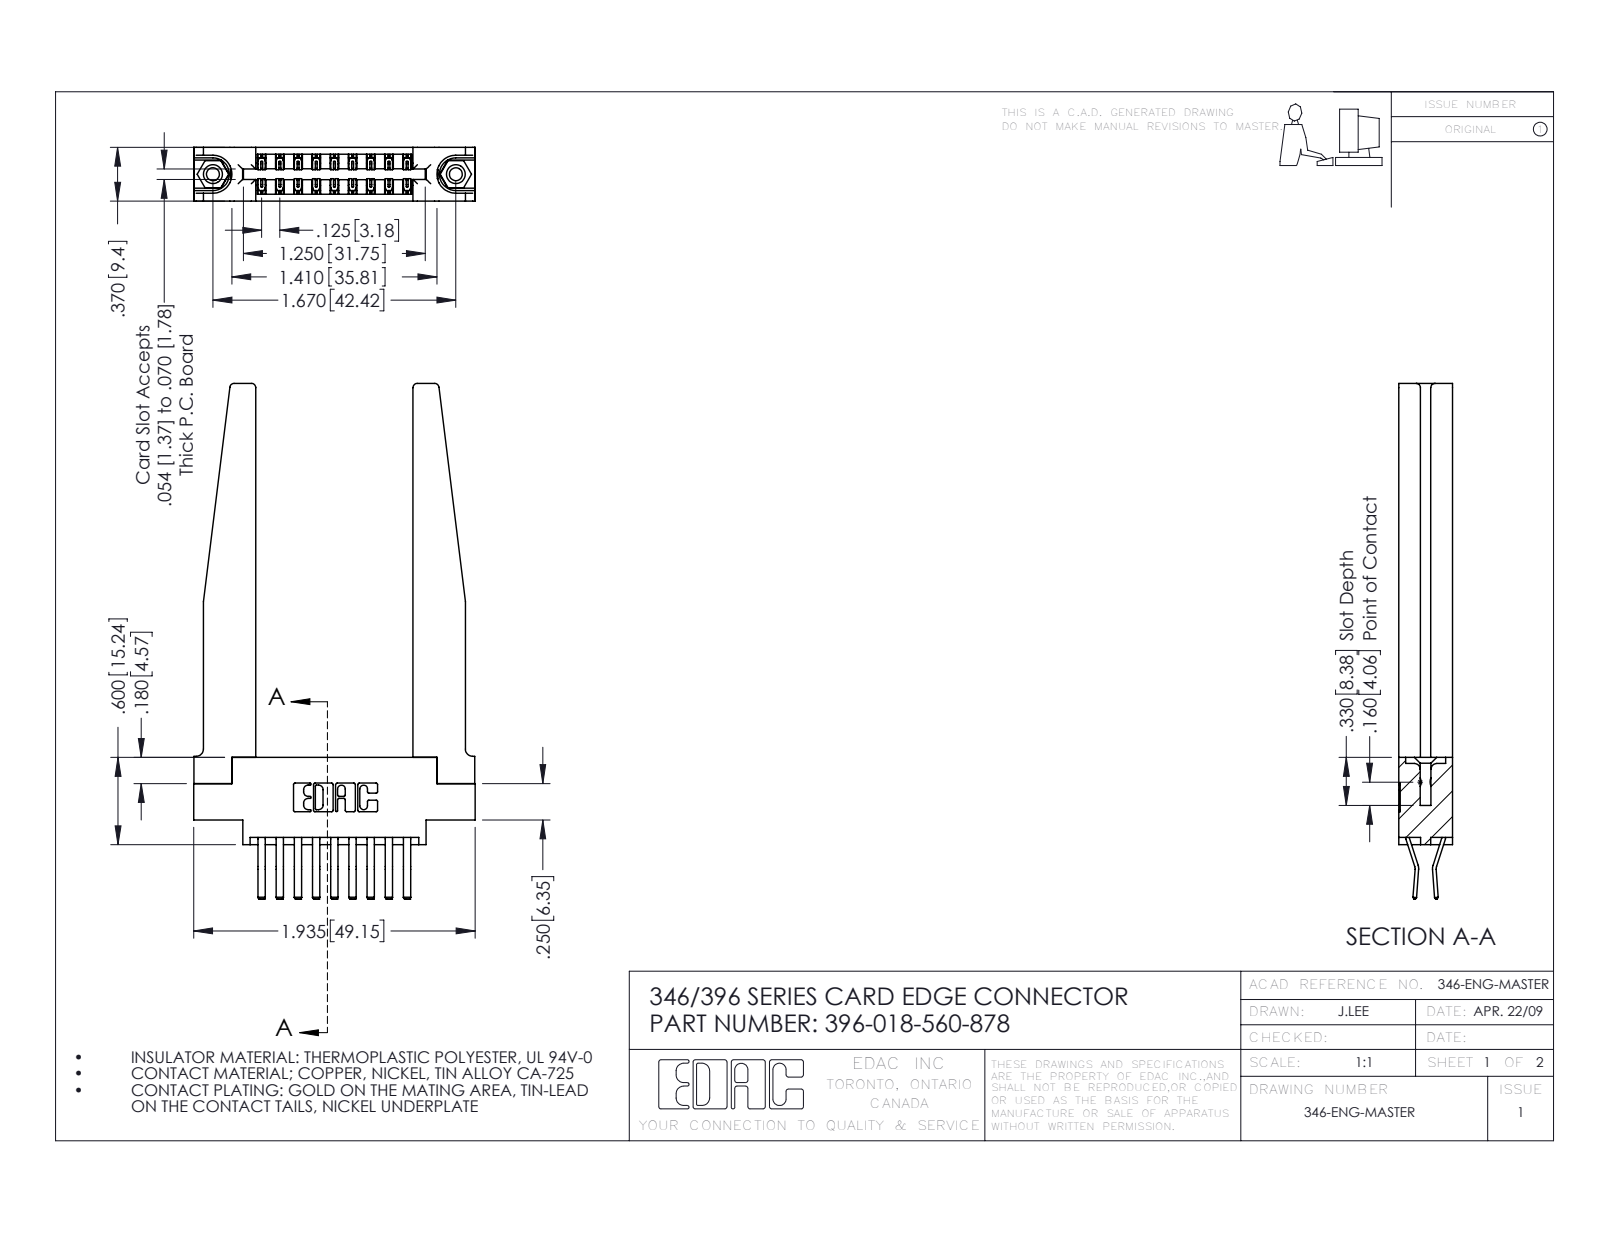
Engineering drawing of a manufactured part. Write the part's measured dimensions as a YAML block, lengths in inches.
part_name: "346-220-078_345-220-078; 346 Part_0.170 Offset - 0.156 Dia-TH; 345-250-001_345-250-001-102; 396-018-560-878 (+1 more)"
step_written_by: "SolidWorks 2016 (CONFIG_CONTROL_DESIGN)"
units: inches
bodies: {solids: 23, faces: 1332, planar: 852, cylindrical: 428, other: 52}
overall_size: [3.545, 1.935, 0.37]
volume: 0.696
surface_area: 19.68
round_holes:
  - {diameter: 0.089, count: 2}
  - {diameter: 0.125, count: 2}
  - {diameter: 0.156, count: 2}
  - {diameter: 0.064, count: 1}
round_bosses_or_shafts:
  - {diameter: 0.155, count: 2}
partial_cylinders:
  - {radius: 0.006, count: 27}
  - {radius: 0.01, count: 22}
  - {radius: 0.03, count: 8}
  - {radius: 0.007, count: 6}
  - {radius: 0.031, count: 6}
  - {radius: 0.05, count: 4}
  - {radius: 0.026, count: 3}
  - {radius: 0.01, count: 2}
face_to_face_distances: [0.37, 0.15, 0.072, 0.148, 0.22, 0.102, 0.048, 0.322, 0.173, 0.25]
hole_center_spacings: [0.246, 1.465, 1.67]
